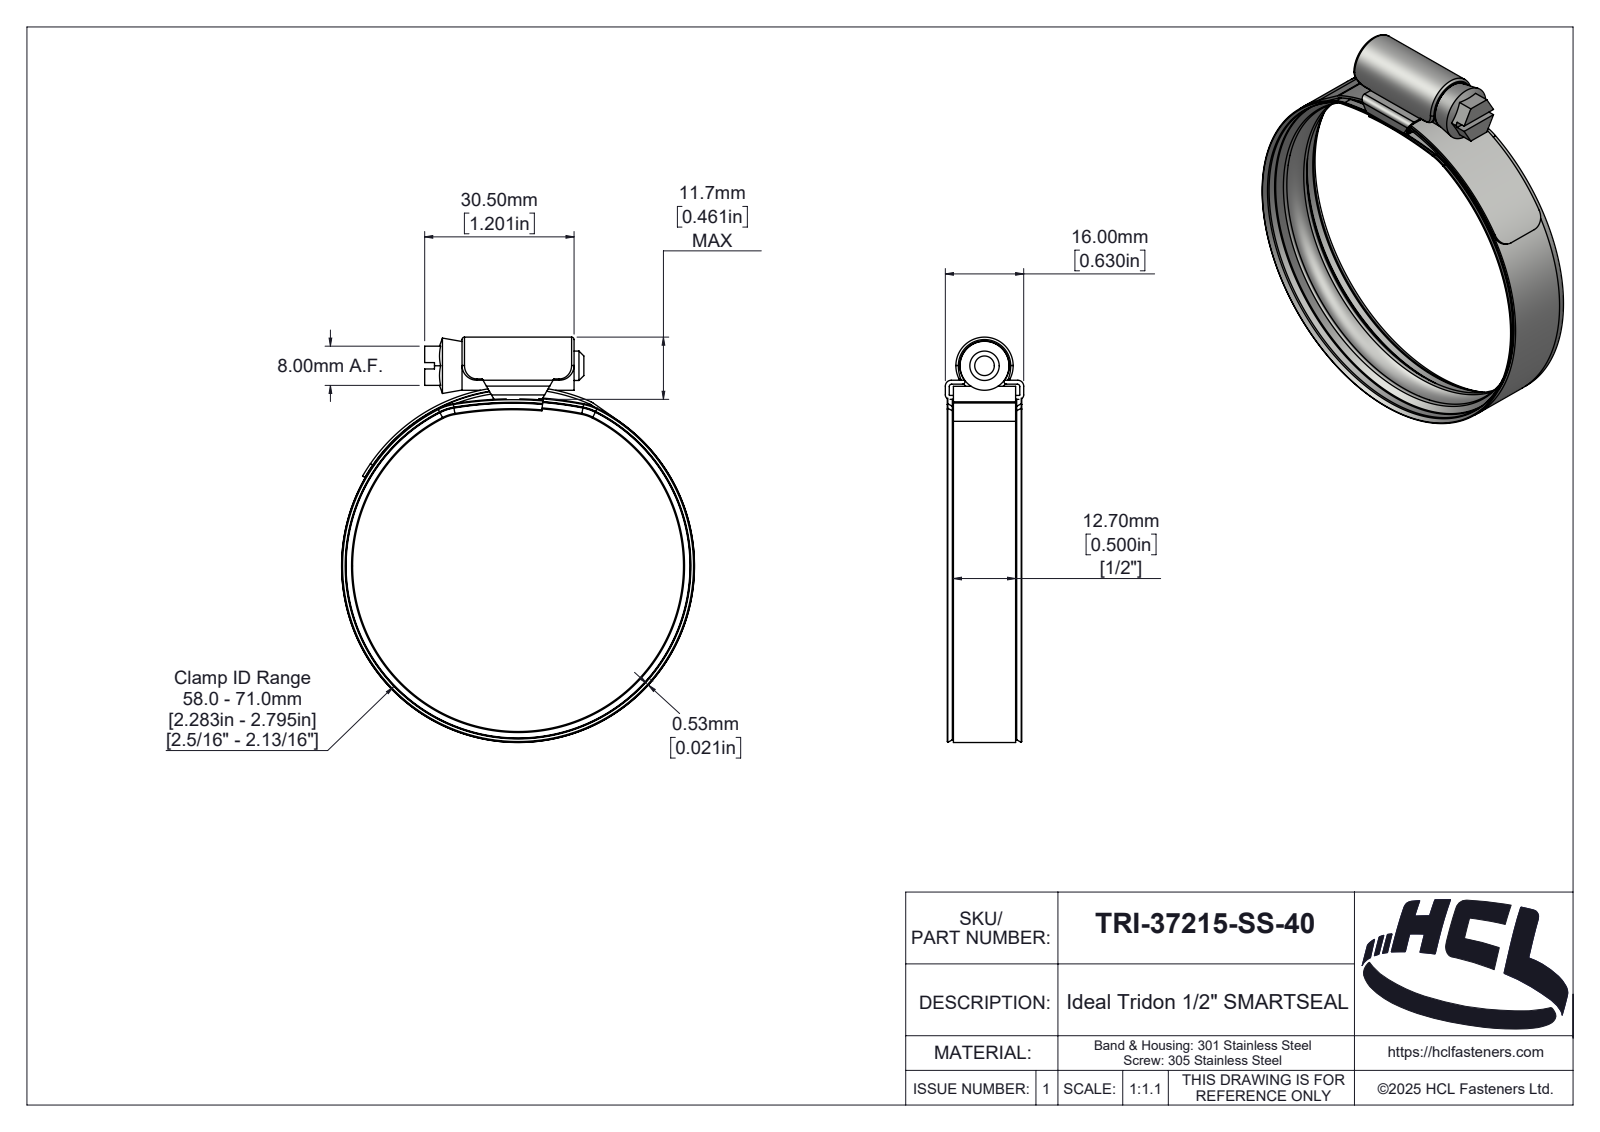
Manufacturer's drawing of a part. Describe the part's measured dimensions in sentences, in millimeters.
The part is named "TRI-37215-SS-40". Its 3-D file was written by "SolidWorks 2025 (AUTOMOTIVE_DESIGN)". It is 4 solids with 418 faces: 42 planar, 119 cylindrical and 257 other. Overall it measures 82.73 by 72.06 by 16 millimeters. Its volume is 5 599 cubic millimeters and its surface area 17 756 square millimeters. Round holes: 1 of diameter 70.4, 1 of diameter 71. Round bosses or shafts: 1 of diameter 72.06, 1 of diameter 70.8, 1 of diameter 10, 1 of diameter 6. Partial cylindrical surfaces (rounded edges, fillets, slot ends): 6 of radius 0.5, 4 of radius 3, 2 of radius 0.1, 2 of radius 0.9, 2 of radius 1.2, 2 of radius 9.9, 2 of radius 10.1, 1 of radius 0.46. The main face-to-face distances are 0.8, 12.7, 3.1, 0.53, 2.3, 30.5, 3.9, 1.65, 14.35, 15.2.
